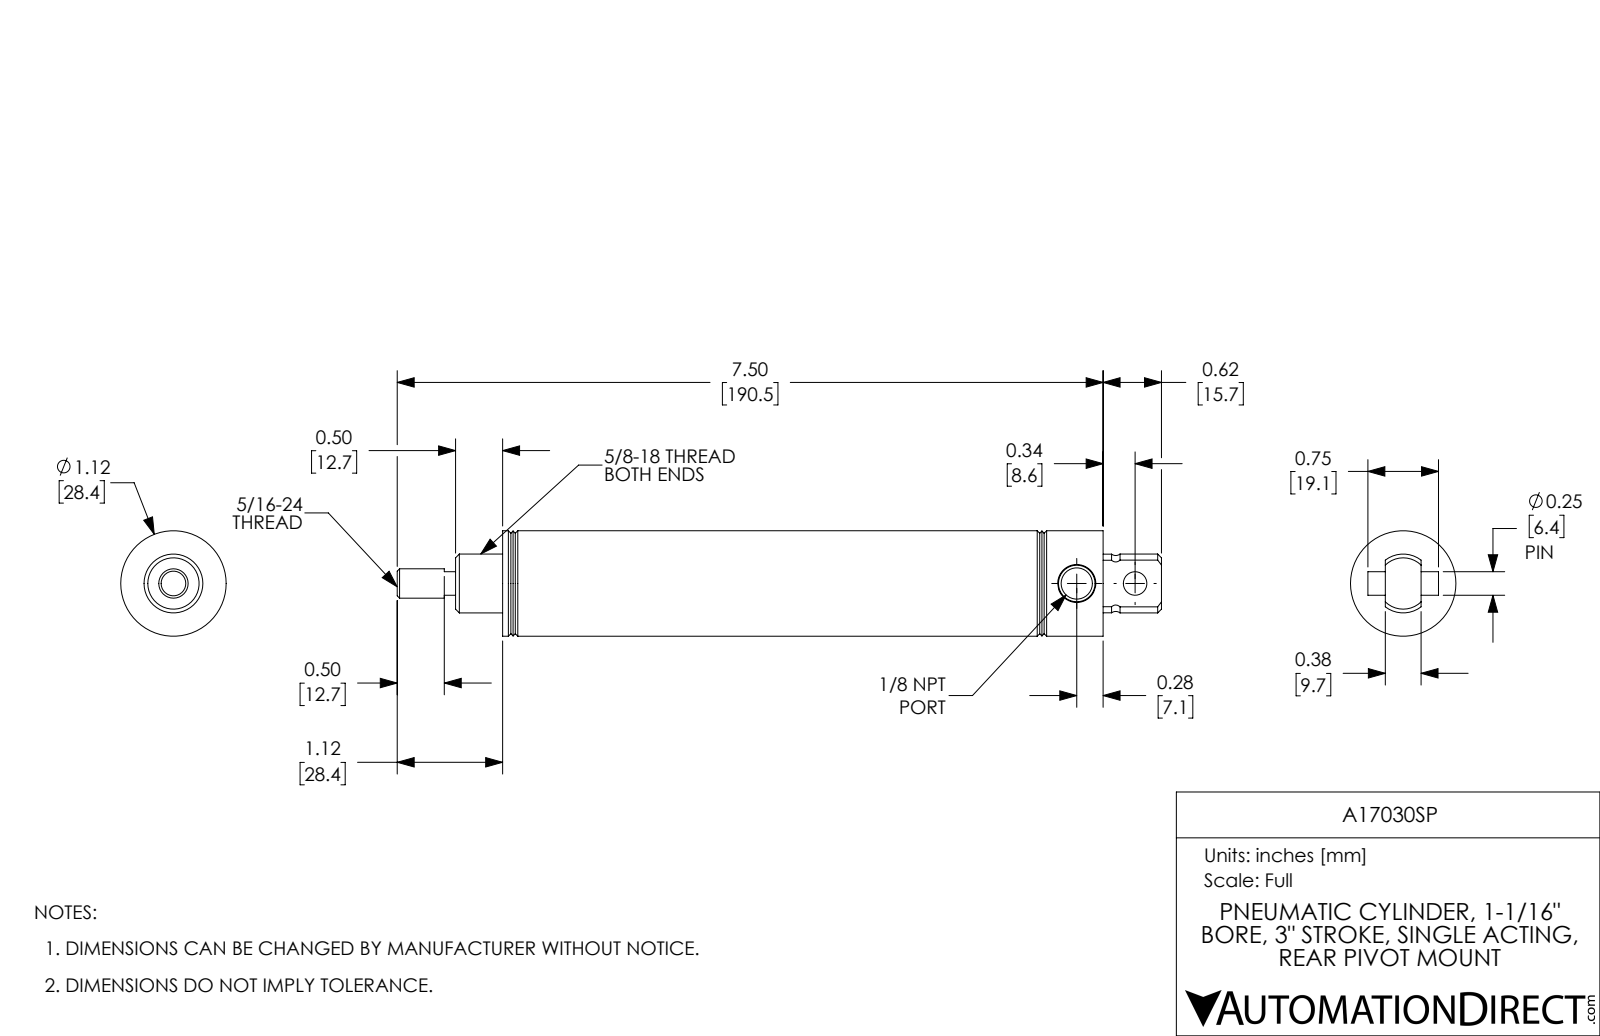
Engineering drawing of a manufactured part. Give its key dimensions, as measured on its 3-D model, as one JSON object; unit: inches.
{"part_name": "A17030SP-MainBody; A17030SP; A17030SP-PIN; A17030SP-Rod", "step_written_by": "SolidWorks 2017 (AUTOMOTIVE_DESIGN)", "units": "inches", "bodies": {"solids": 3, "faces": 76, "planar": 20, "cylindrical": 26, "other": 30}, "overall_size": [8.12, 1.12, 1.12], "volume_in3": 4.146, "surface_area_in2": 52.21, "round_holes": [[0.25, 1], [0.312, 1], [0.332, 1], [1.063, 1]], "round_bosses_or_shafts": [[1.12, 1], [0.625, 1]], "partial_cylinders_radius": [[0.311, 1], [0.313, 1]], "face_to_face_distances": [0.5, 4.94, 3.5, 3, 1.44, 1.94, 4.94, 6.38, 4.44, 1.44], "hole_center_spacings": [0.62]}
